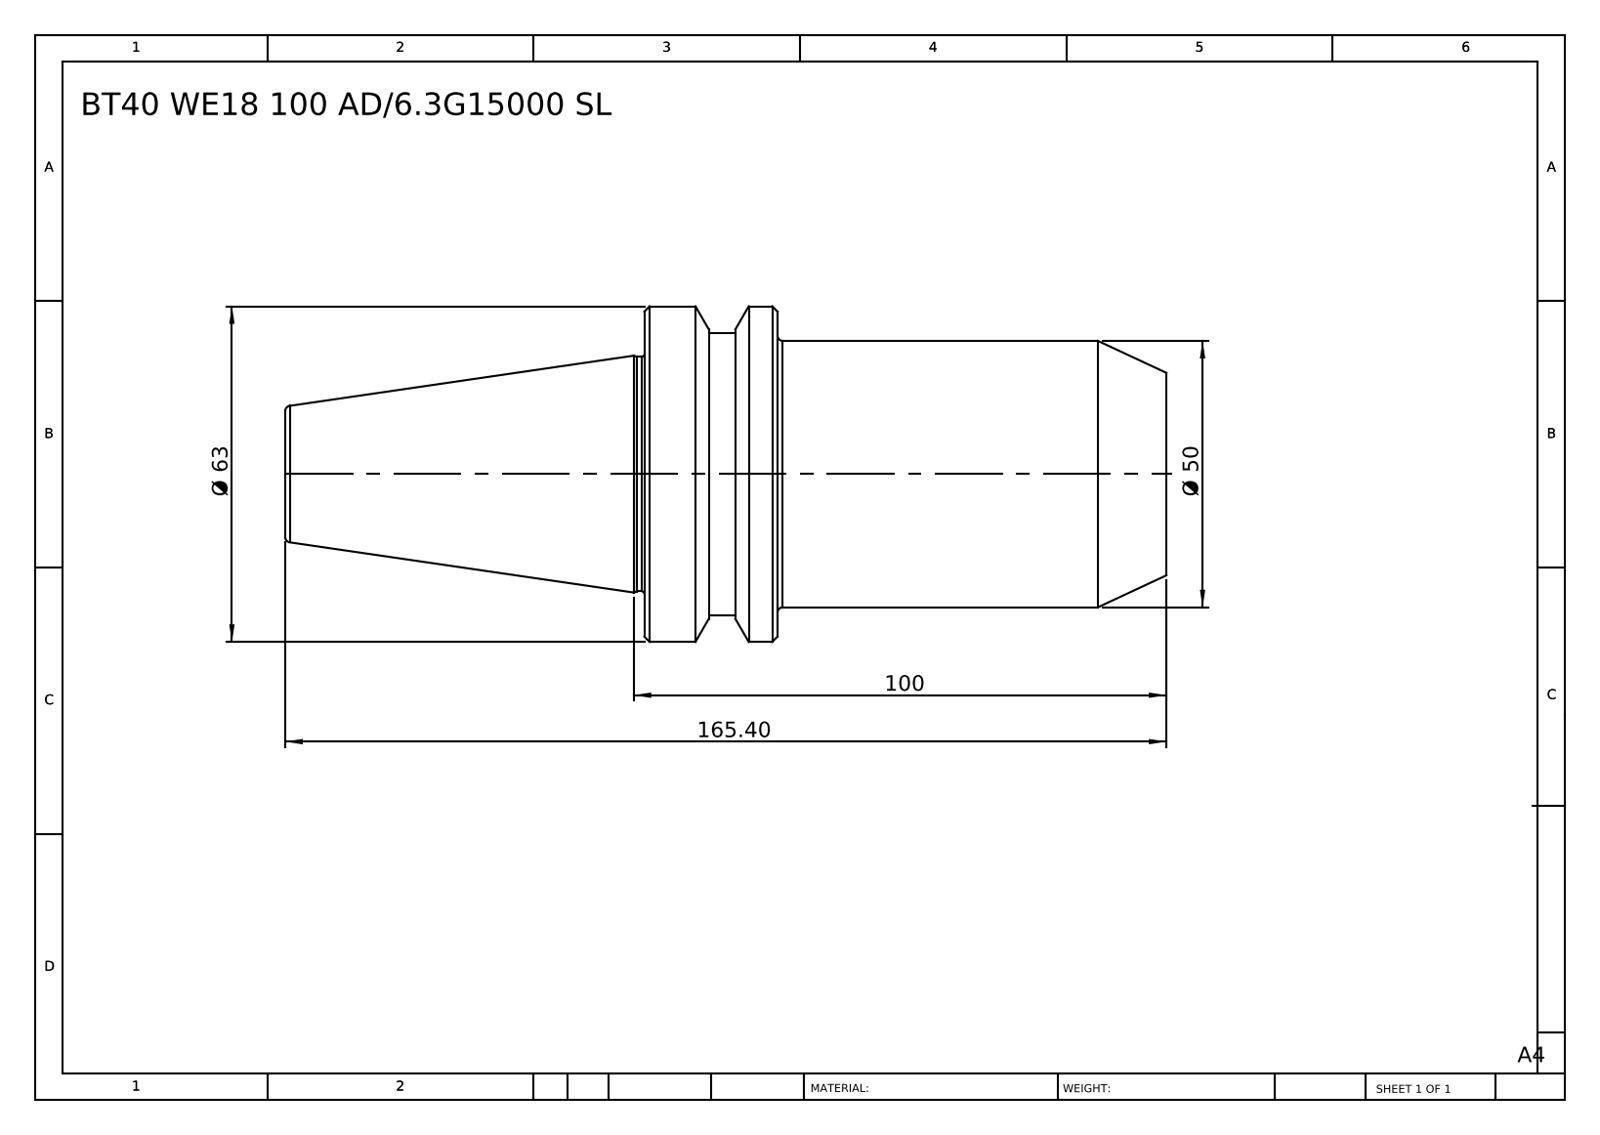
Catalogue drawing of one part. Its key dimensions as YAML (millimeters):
part_name: "BT40 WE18 100 AD-6.3G15000 SL"
step_written_by: "SolidWorks 2014 (CONFIG_CONTROL_DESIGN)"
units: millimeters
bodies: {solids: 1, faces: 38, planar: 6, cylindrical: 10, other: 22}
overall_size: [165.4, 63, 63]
volume: 276138
surface_area: 28844
round_bosses_or_shafts:
  - {diameter: 63, count: 1}
  - {diameter: 53, count: 1}
  - {diameter: 50, count: 1}
  - {diameter: 44, count: 1}
face_to_face_distances: [98, 73, 25, 165.4, 92.4, 67.4, 85.9, 12.9, 12.1, 79.5]
